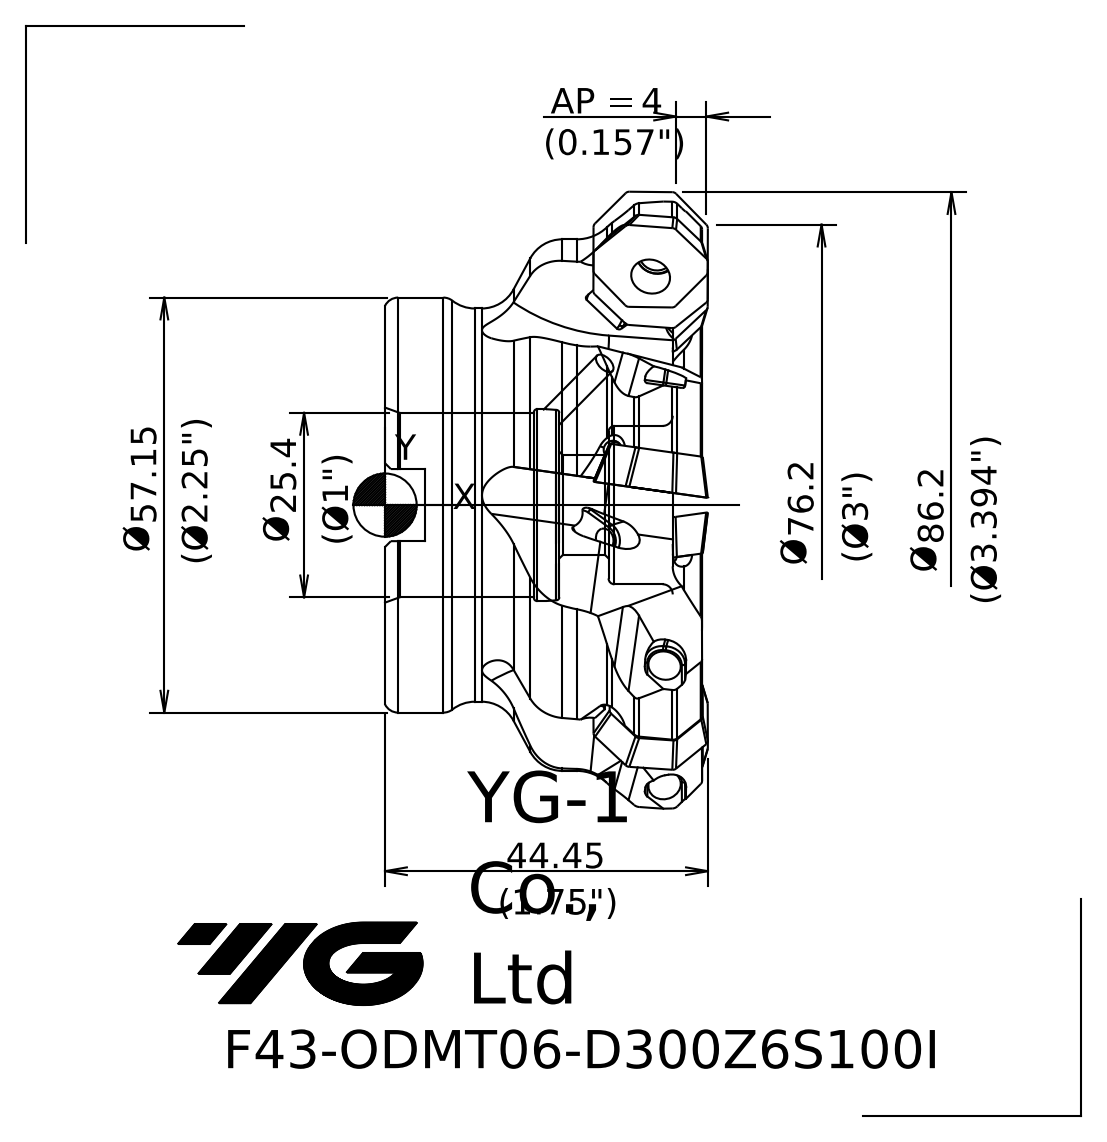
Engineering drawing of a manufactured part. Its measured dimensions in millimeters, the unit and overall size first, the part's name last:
Units: millimetres
Overall size (bounding box): 86.31 × 86.31 × 44.45
Round holes (diameter × count): ⌀13.7 ×1, ⌀21.8 ×1, ⌀25.4 ×1, ⌀26.4 ×1
Round bosses / shafts (diameter × count): ⌀84.22 ×1, ⌀73.2 ×1, ⌀57.15 ×1, ⌀54.15 ×1
Main face-to-face distances: 39.61, 15.61, 24, 34.05, 18.44, 5.56, 9.93, 8.83, 6.78, 25.22
Volume: 133 756 mm³ · Surface area: 32 654 mm²
Bodies: 1 solid, 66 faces (16 planar, 8 cylindrical, 42 other)
Part name (STEP PRODUCT): 1022133874A4w6s0
STEP written by: SIEMENS PLM Software NX 10.0 (AP203_CONFIGURATION_CONTROLLED_3D_DESIGN_OF_MECHANICAL_PARTS_AND_ASSEMBLIES_MIM_LF)
